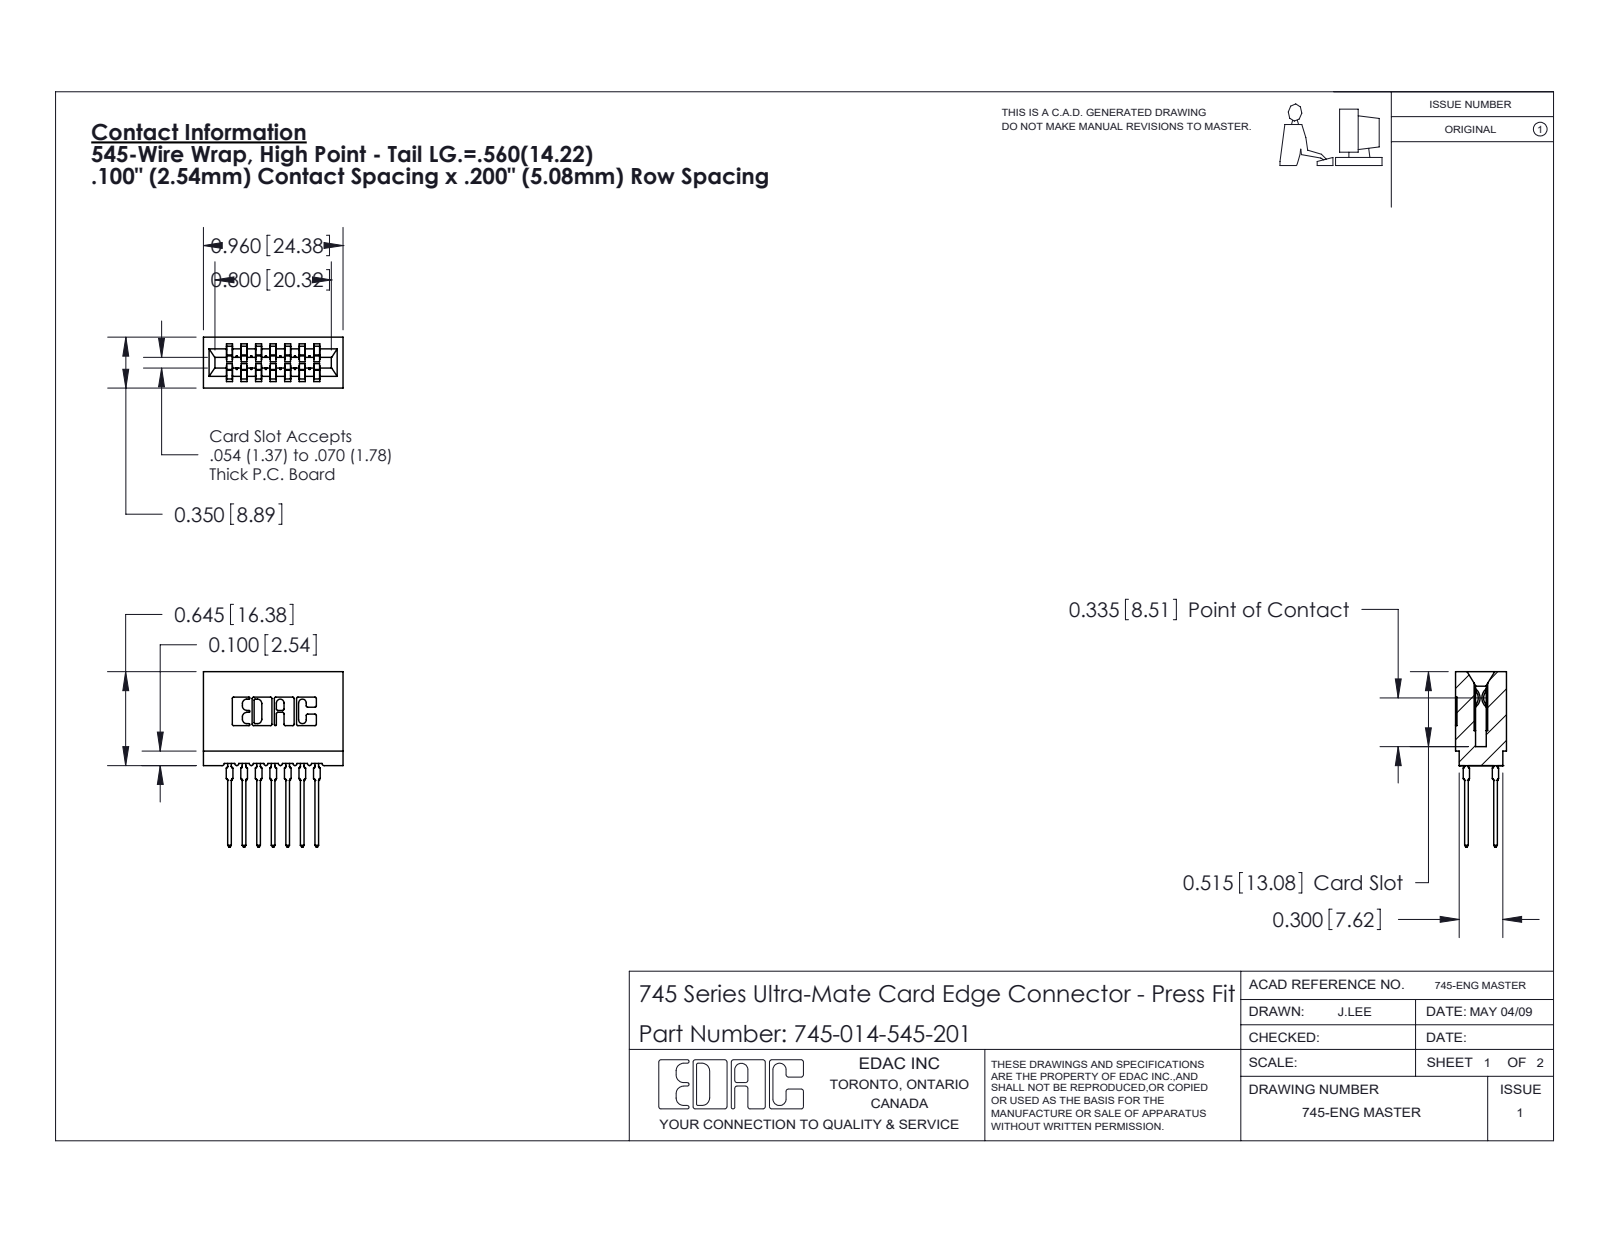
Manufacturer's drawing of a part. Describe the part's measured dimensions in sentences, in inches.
The part is named "745 Part_Insulator Option - 01; 745-292-001_545; 745-014-545-201". Its 3-D file was written by "SolidWorks 2020 (CONFIG_CONTROL_DESIGN)". It is 15 solids with 1348 faces: 699 planar, 285 cylindrical and 364 other. Overall it measures 1.206 by 0.96 by 0.35 inches. Its volume is 0.15 cubic inches and its surface area 6.816 square inches. Partial cylindrical surfaces (rounded edges, fillets, slot ends): 28 of radius 0.021, 22 of radius 0.01, 14 of radius 0.015, 8 of radius 0.005, 8 of radius 0.011, 6 of radius 0.007, 6 of radius 0.031, 3 of radius 0.026. The main face-to-face distances are 0.1, 0.2, 0.3, 0.042, 0.142, 0.4, 0.058, 0.242, 0.158, 0.063.
